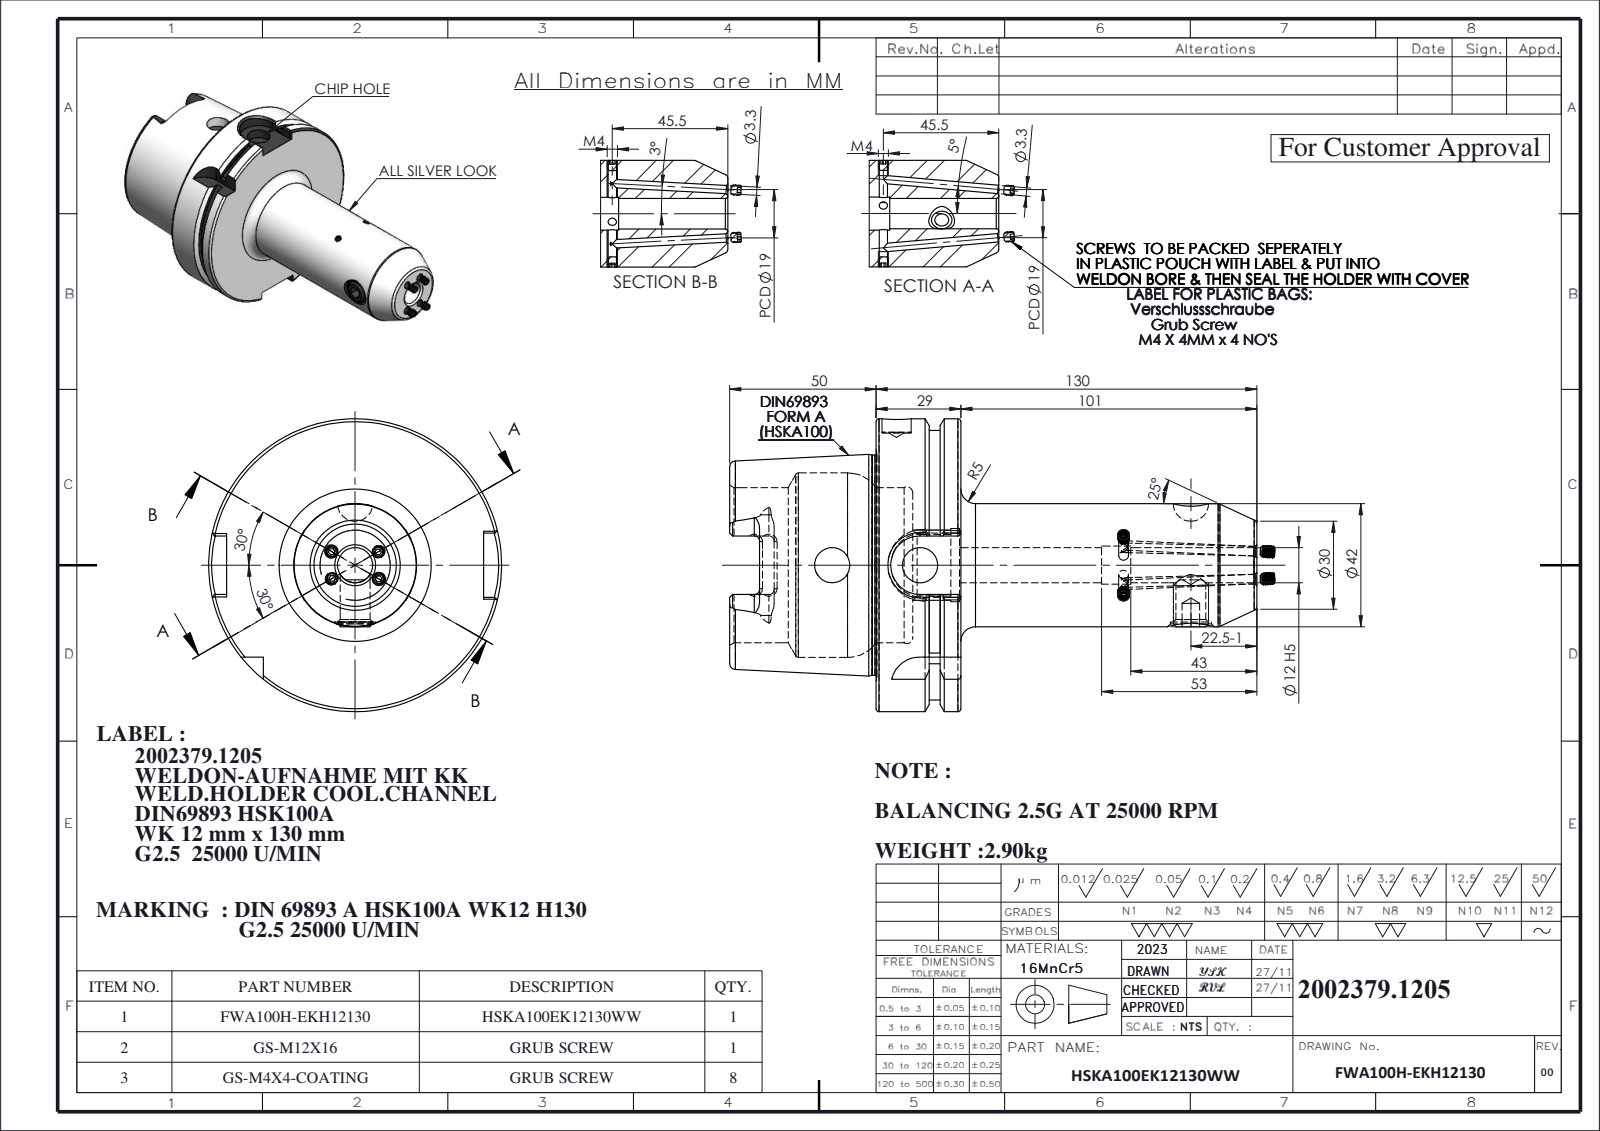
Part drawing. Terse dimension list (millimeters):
name: FWA100H-EKH12130; HSKA100EK12130WW; GS-M12X16-DIN1835-B; GS-M4X4_DIN 913 - M4 x 4-N
written by: SolidWorks 2023 (CONFIG_CONTROL_DESIGN)
unit: mm
bodies: 10 solids, 628 faces (140 planar, 166 cylindrical, 322 other)
size: 186.17 × 100 × 100
volume: 376 007 mm³; area: 70 228 mm²
holes: 7× ⌀3.3, 3× ⌀12, 1× ⌀10, 1× ⌀10.2, 1× ⌀13, 1× ⌀14, 1× ⌀21, 1× ⌀25, 1× ⌀53, 1× ⌀63
bosses: 7× ⌀4, 1× ⌀100, 1× ⌀92, 1× ⌀75.16, 1× ⌀42, 1× ⌀12
rounds: 6× R1.8, 4× R4.88, 2× R10, 1× R11
face distances: 28.95, 12.5, 16.45, 50, 62.5, 78.95, 16, 180, 130, 117.5
hole spacings: 30, 100.5
